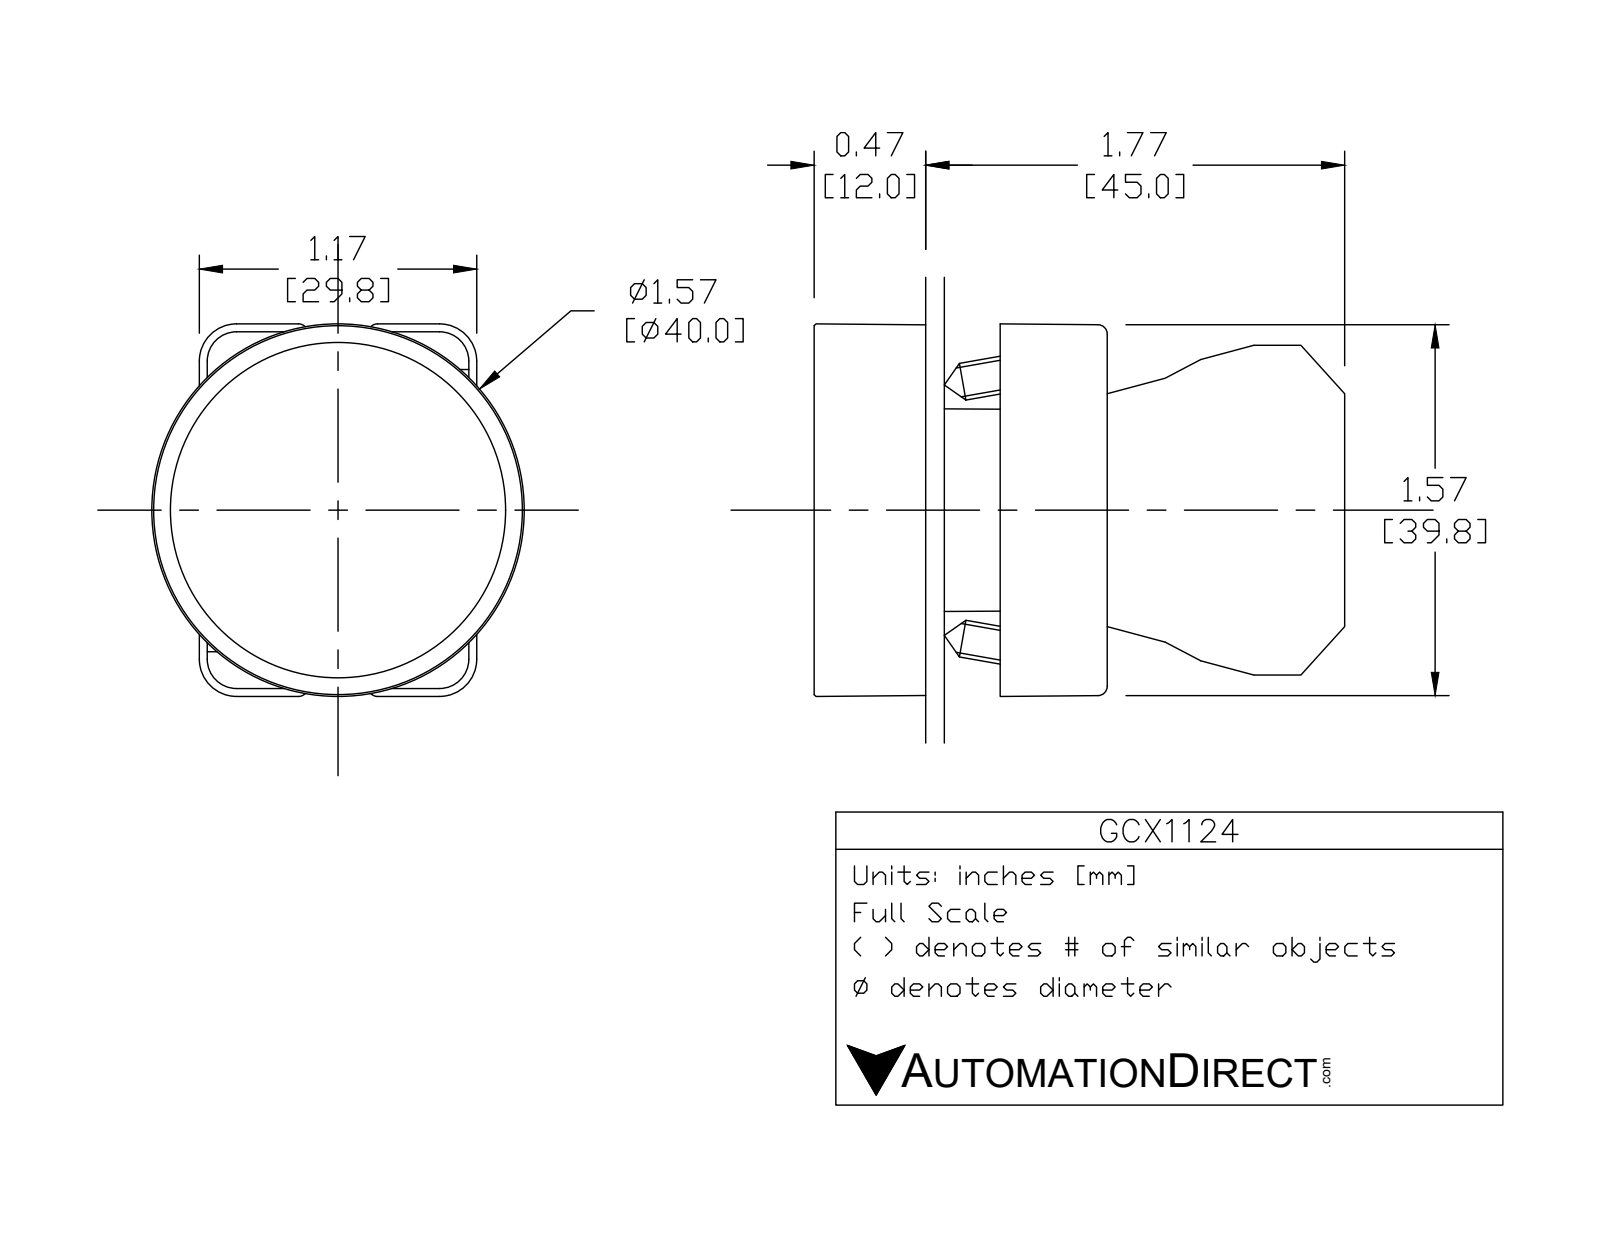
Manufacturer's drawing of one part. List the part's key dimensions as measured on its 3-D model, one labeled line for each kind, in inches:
Part name (STEP PRODUCT): ecx1029; ecx1040; GCX1124 OPERATOR; GCX1124
STEP written by: SolidWorks 2016 (AUTOMOTIVE_DESIGN)
Units: inches
Bodies: 6 solids, 381 faces (222 planar, 132 cylindrical, 27 other)
Overall size (bounding box): 2.217 × 1.581 × 1.569
Volume: 2.153 in³ · Surface area: 32.09 in²
Round holes (diameter × count): ⌀0.079 ×2, ⌀0.124 ×2, ⌀0.13 ×2, ⌀0.087 ×1, ⌀0.197 ×1, ⌀0.878 ×1, ⌀0.888 ×1, ⌀1.417 ×1
Round bosses / shafts (diameter × count): ⌀0.157 ×2, ⌀1.569 ×1, ⌀1.398 ×1, ⌀0.945 ×1, ⌀0.856 ×1, ⌀0.78 ×1
Partial cylindrical surfaces — rounded edges, fillets, slot ends (radius × count): R0.059 ×24, R0.041 ×12, R0.124 ×12, R0.157 ×12, R0.039 ×4, R0.128 ×2, R0.02 ×1, R0.063 ×1
Main face-to-face distances: 0.472, 0.72, 1.193, 0.579, 0.7, 0.02, 0.493, 0.033, 0.031, 0.689
Hole centre spacings: 0.236, 0.544, 0.472, 0.49
